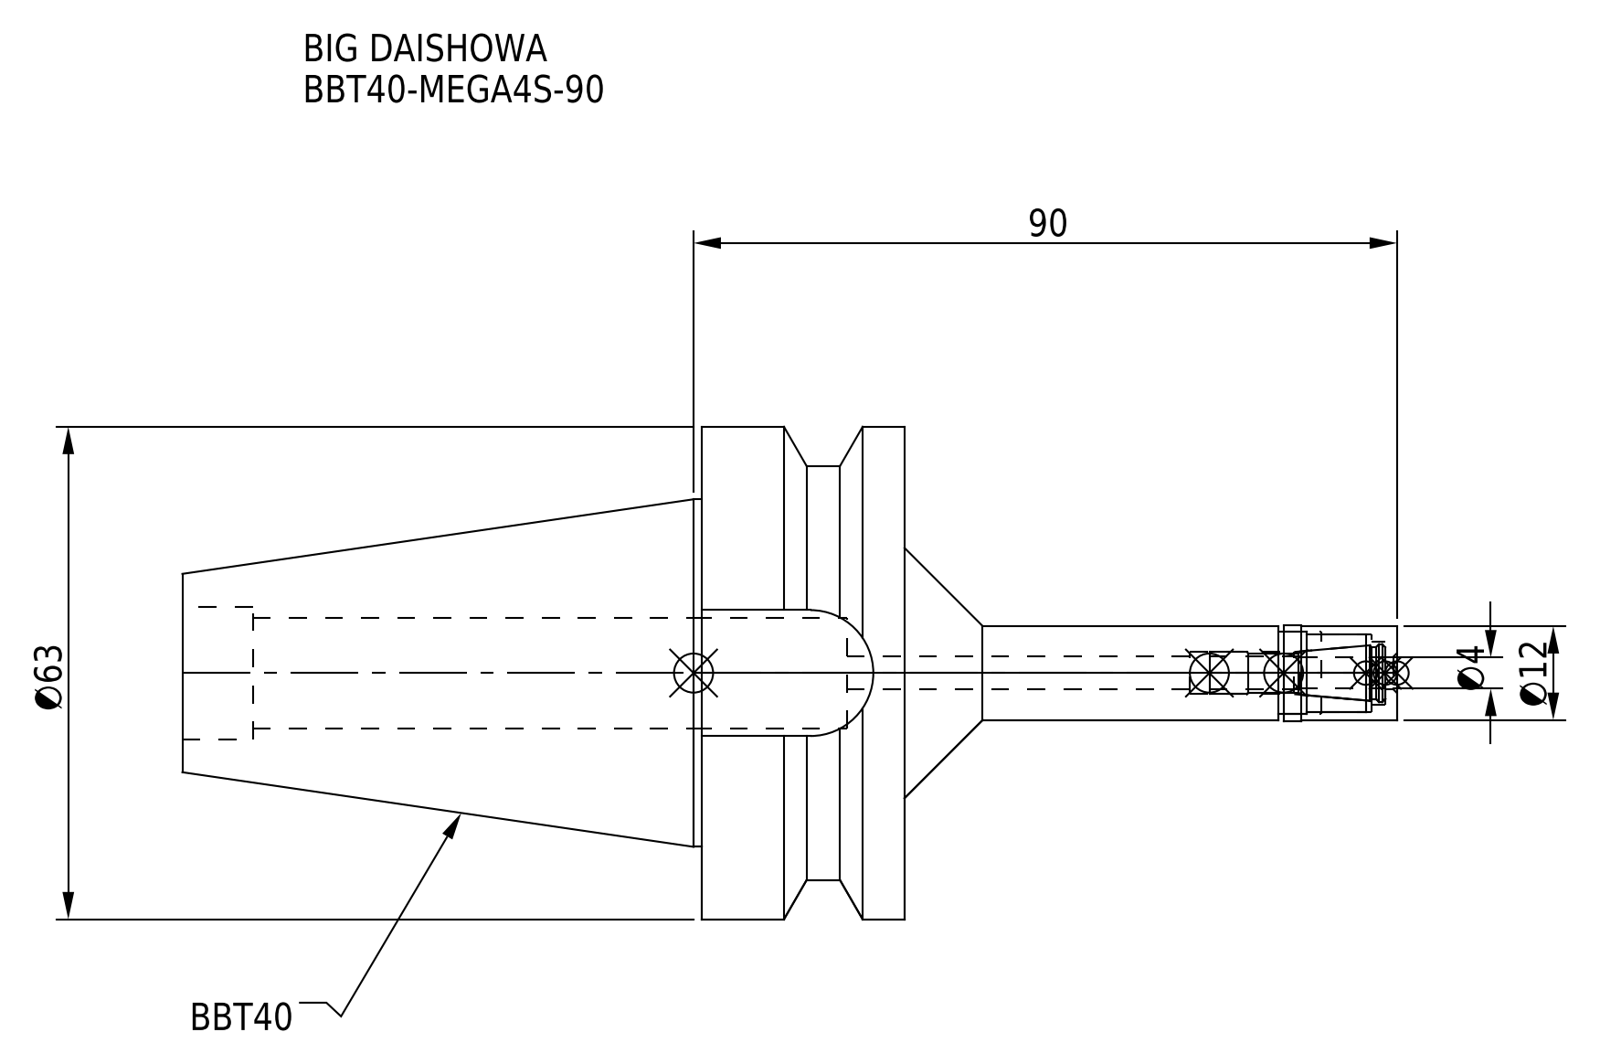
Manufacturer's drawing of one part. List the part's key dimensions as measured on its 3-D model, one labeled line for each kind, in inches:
Part name (STEP PRODUCT): BBT40-MEGA4S-90-040.stp; BBT40-MEGA4S-90; BBT40-MEGA4S-90_1.stp; MGN4S_1.stp (+3 more)
STEP written by: SolidWorks 2019 (CONFIG_CONTROL_DESIGN)
Units: inches
Bodies: 2 solids, 71 faces (21 planar, 38 cylindrical, 12 other)
Overall size (bounding box): 6.118 × 2.48 × 2.48
Volume: 7.944 in³ · Surface area: 41.65 in²
Round holes (diameter × count): ⌀0.161 ×1, ⌀0.165 ×1, ⌀0.213 ×1, ⌀0.315 ×1, ⌀0.394 ×1, ⌀0.413 ×1, ⌀0.559 ×1, ⌀0.669 ×1
Round bosses / shafts (diameter × count): ⌀2.48 ×1, ⌀2.087 ×1, ⌀1.75 ×1, ⌀0.484 ×1, ⌀0.472 ×1
Partial cylindrical surfaces — rounded edges, fillets, slot ends (radius × count): R0.317 ×1
Main face-to-face distances: 1.024, 1.772, 2.614, 3.638, 0.634, 3.346, 0.291, 0.732, 2.48, 2.772
